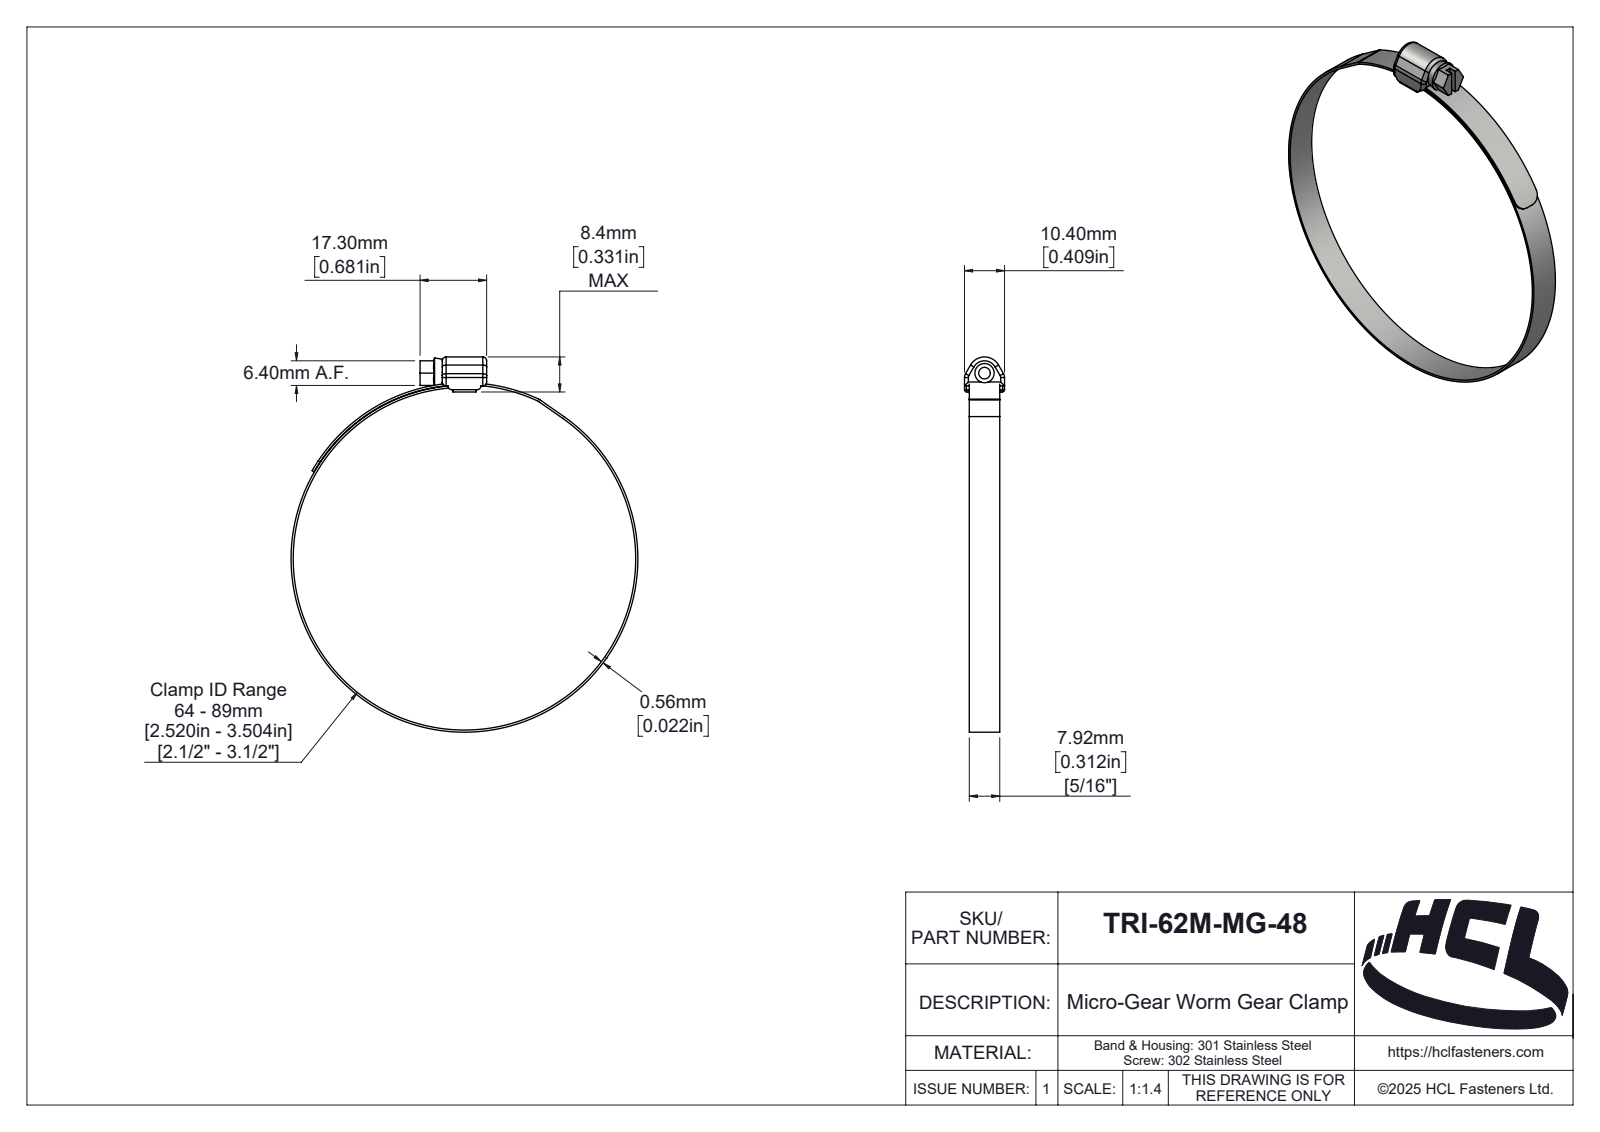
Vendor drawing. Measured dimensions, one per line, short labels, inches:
name: TRI-62M-MG-48
written by: SolidWorks 2025 (AUTOMOTIVE_DESIGN)
unit: in
bodies: 3 solids, 186 faces (38 planar, 87 cylindrical, 61 other)
size: 3.837 × 3.548 × 0.409
volume: 0.147 in³; area: 10.46 in²
holes: 1× ⌀0.197, 1× ⌀3.504
bosses: 1× ⌀3.548
rounds: 12× R0.039, 3× R0.079, 2× R0.004, 2× R0.024, 2× R0.118, 1× R0.01, 1× R0.04, 1× R0.05
face distances: 0.312, 0.043, 0.02, 0.022, 0.049, 0.361, 0.063, 0.244, 0.409, 0.227
